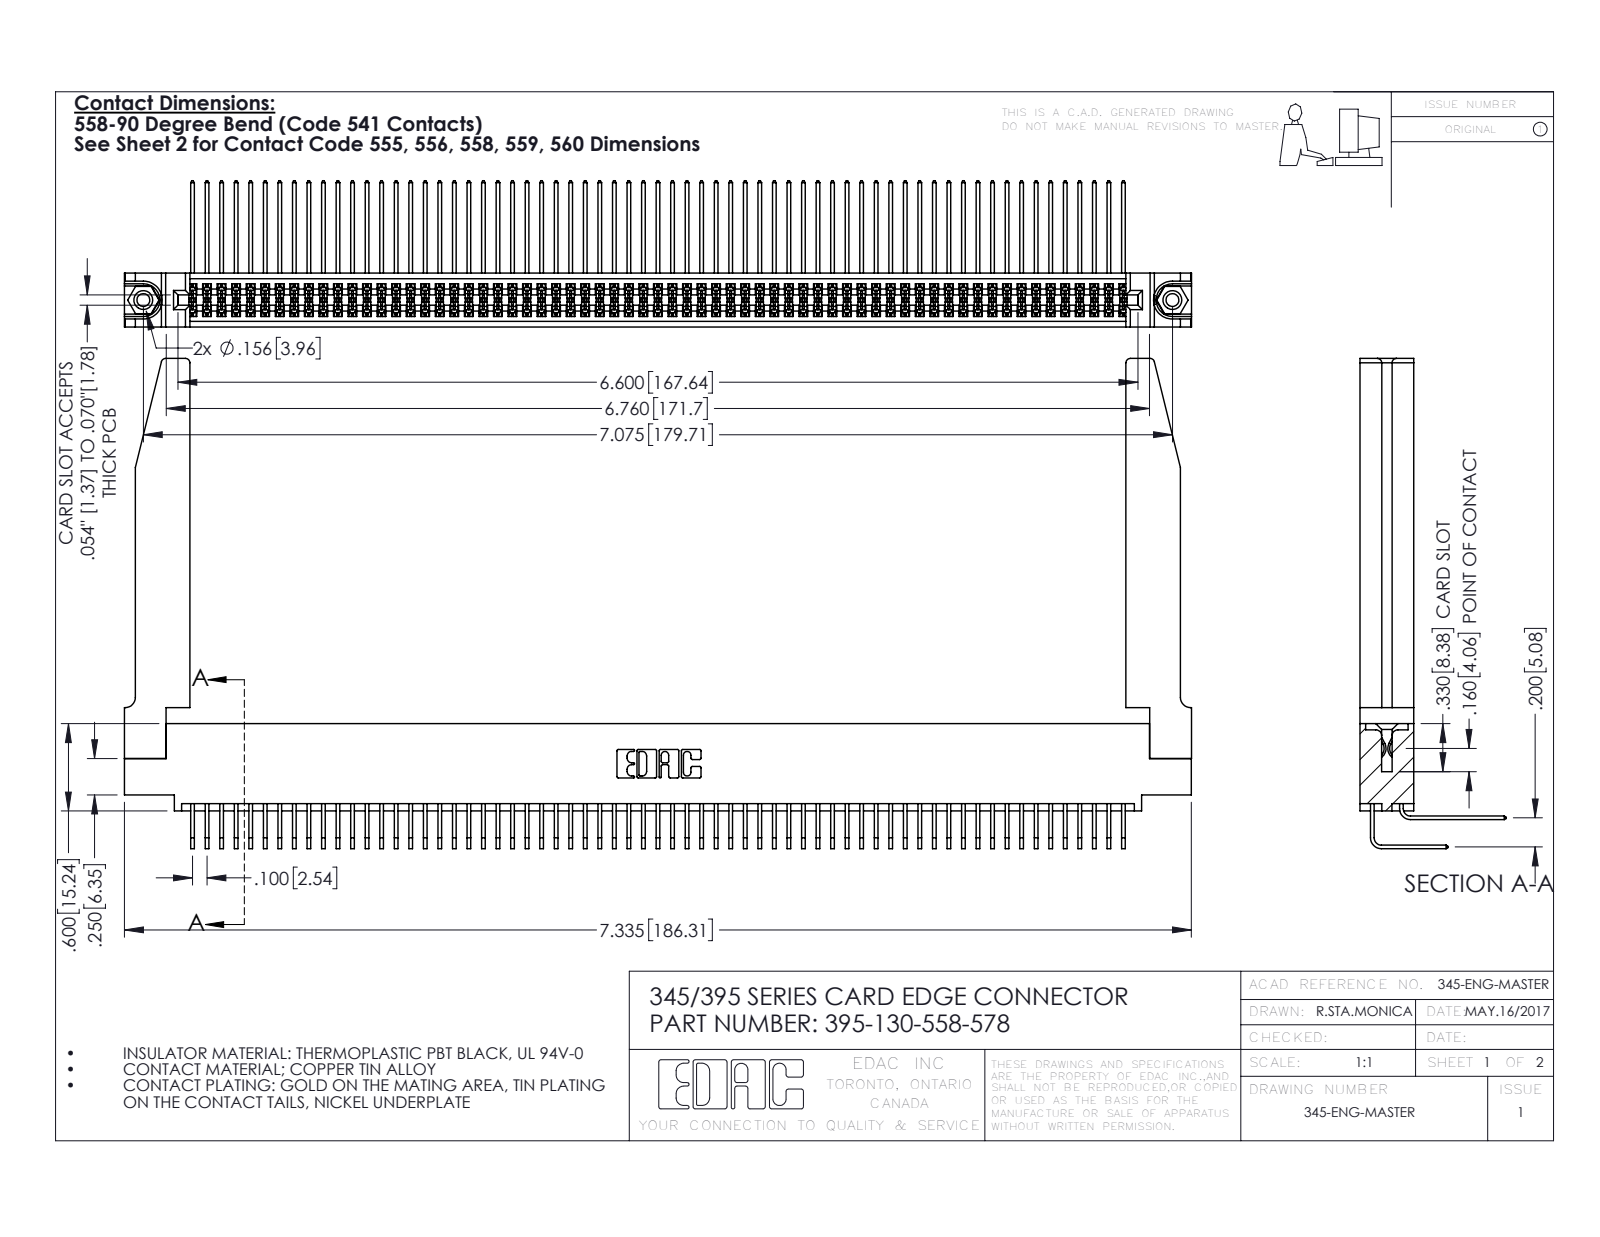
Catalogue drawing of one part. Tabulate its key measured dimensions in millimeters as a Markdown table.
| quantity | value |
| --- | --- |
| part name | 345 Part_0.110 Offset - 0.156 Dia-TH; 345-292-001_558 559 Tail - 1; 345-292-001_558 Tail - 2; 395-130-558-578 (+2 more) |
| STEP written by | SolidWorks 2016 (CONFIG_CONTROL_DESIGN) |
| units | millimeters |
| bodies | 135 solids, 7124 faces (4776 planar, 2296 cylindrical, 52 other) |
| overall size | 186.3 × 85.6 × 25.5 |
| volume | 26 760 mm³ |
| surface area | 38 970 mm² |
| round holes (diameter × count) | 2.3 × 2, 3.2 × 2, 4 × 2, 1.6 × 1 |
| round bosses / shafts (diameter × count) | 3.9 × 2 |
| partial cylindrical surfaces (radius × count) | 0.2 × 196, 0.3 × 22, 0.8 × 8, 0.2 × 6, 0.8 × 6, 0.7 × 3, 0.4 × 2, 0.5 × 2 |
| main face-to-face distances | 1.8, 7.6, 9.4, 5.1, 2.5, 6.9, 0.6, 5.7, 0.6, 4.4 |
| hole center spacings | 6.9, 173.7, 179.7 |
